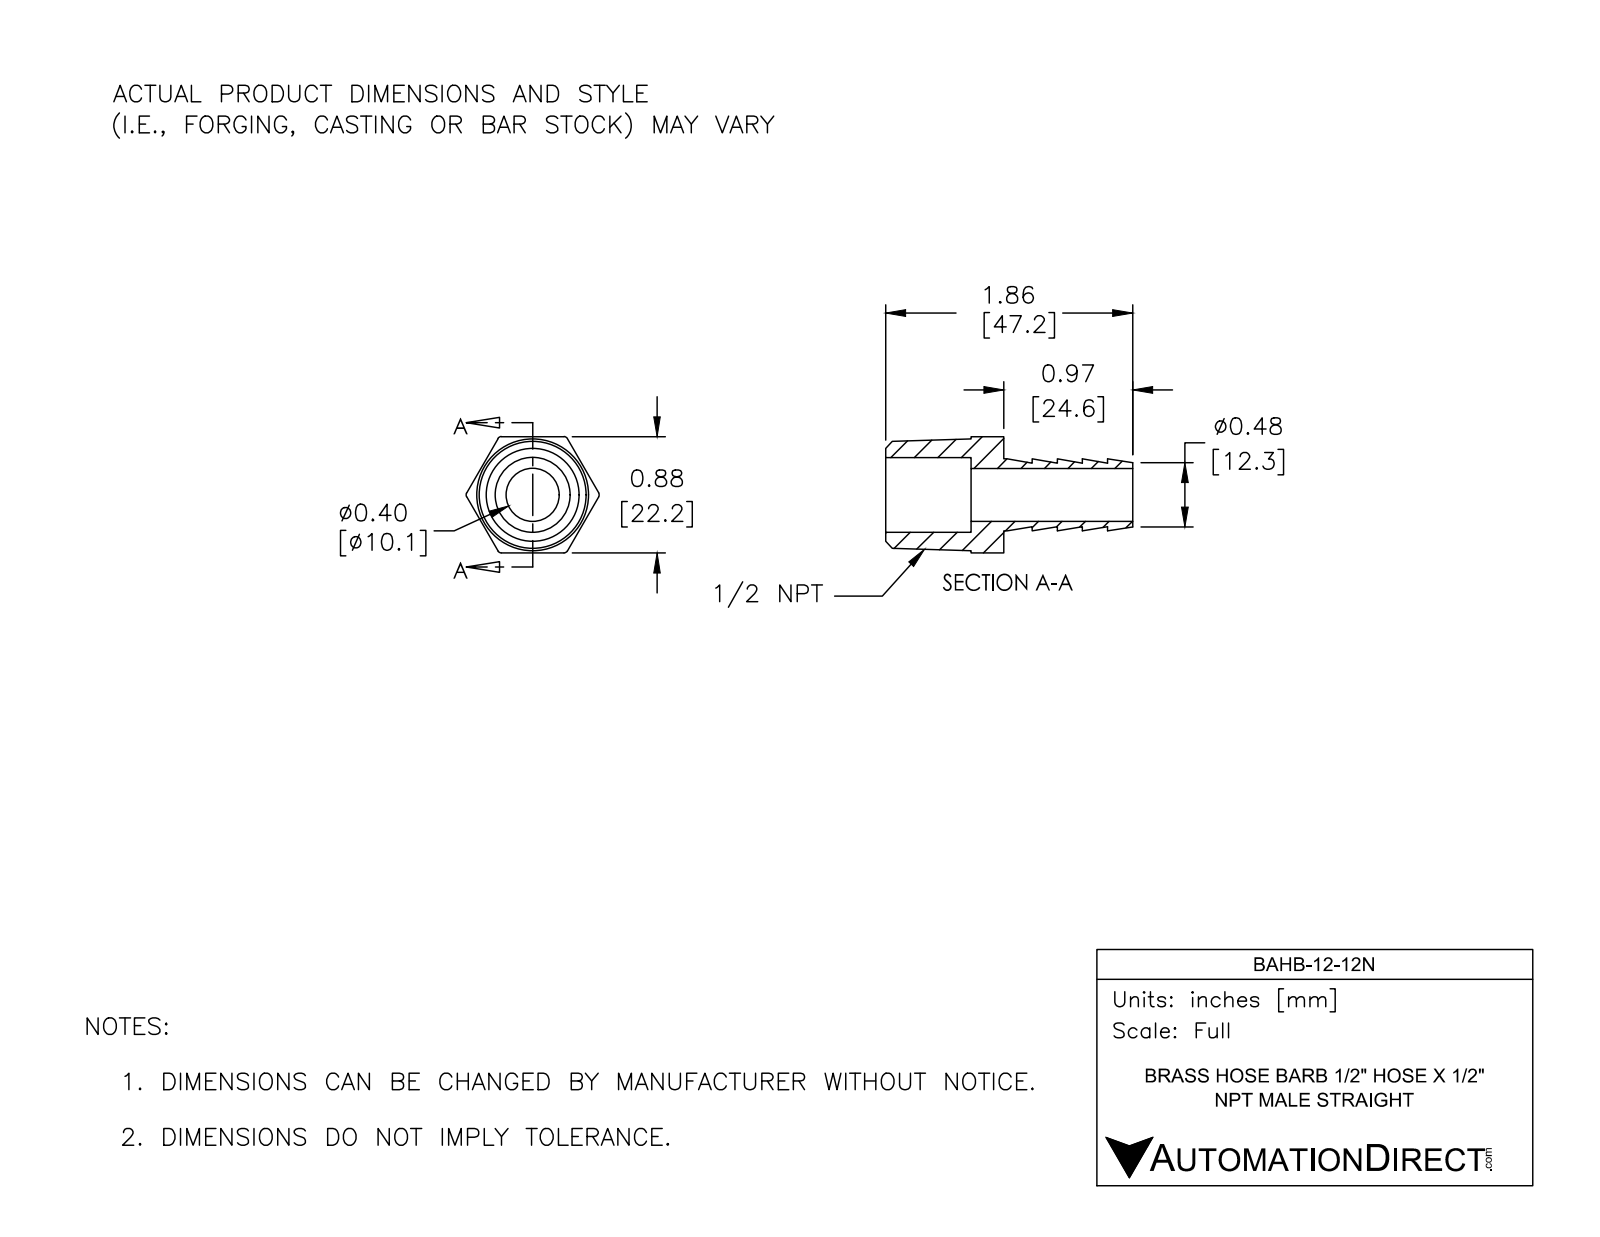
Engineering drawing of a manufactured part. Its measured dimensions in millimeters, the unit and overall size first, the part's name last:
Units: millimetres
Overall size (bounding box): 47.2 × 25.4 × 22.2
Round holes (diameter × count): ⌀10.1 ×1, ⌀14.3 ×1
Round bosses / shafts (diameter × count): ⌀13.8 ×1
Partial cylindrical surfaces — rounded edges, fillets, slot ends (radius × count): R0.8 ×6
Main face-to-face distances: 22.2, 6.3, 4.8, 9.6, 22.6, 16.3, 14.4, 24.6, 30.9, 47.2
Volume: 6 390 mm³ · Surface area: 4 992 mm²
Bodies: 1 solid, 41 faces (15 planar, 12 cylindrical, 14 other)
Part name (STEP PRODUCT): BAHB-12-12N
STEP written by: SolidWorks 2017 (AUTOMOTIVE_DESIGN)
